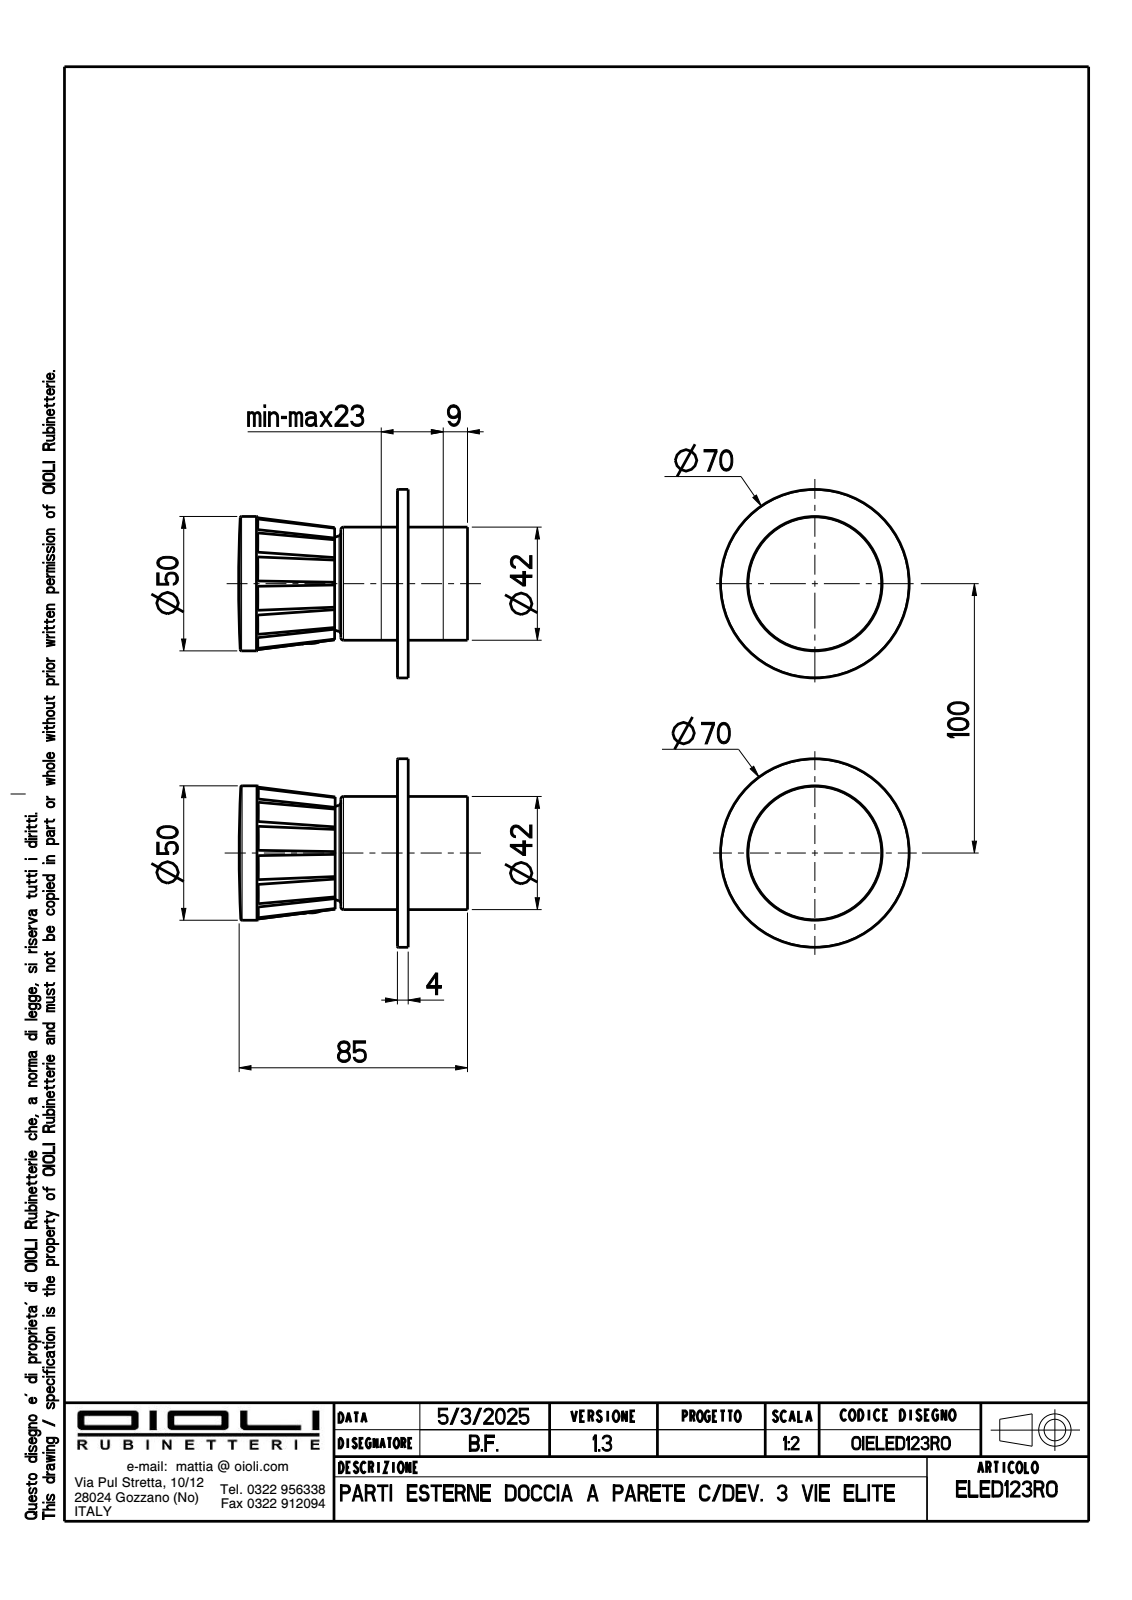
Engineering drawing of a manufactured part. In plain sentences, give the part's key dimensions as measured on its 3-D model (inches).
The part is named "OIBR00949; OIBR00242; OIOR00091; OIBR00948 (+2 more)". Its 3-D file was written by "CREO PARAMETRIC BY PTC INC, 2024493 (CONFIG_CONTROL_DESIGN)". It is 10 solids with 314 faces: 122 planar, 96 cylindrical and 96 other. Overall it measures 6.693 by 3.343 by 2.756 inches. Its volume is 5.389 cubic inches and its surface area 114.8 square inches. Round holes: 2 of diameter 0.157, 2 of diameter 0.165, 2 of diameter 0.209, 2 of diameter 0.256, 2 of diameter 0.374, 2 of diameter 1.181, 2 of diameter 1.555, 2 of diameter 1.575, 2 of diameter 1.677, 2 of diameter 1.791. Round bosses or shafts: 2 of diameter 2.756, 2 of diameter 1.965, 2 of diameter 1.654, 2 of diameter 0.65, 2 of diameter 0.197. Partial cylindrical surfaces (rounded edges, fillets, slot ends): 20 of radius 0.004, 4 of radius 0.268. The main face-to-face distances are 0.157, 2.346, 2.354, 2.189, 2.197, 0.512, 0.669, 1.677, 1.685, 0.083. The hole center spacings are 3.937.
